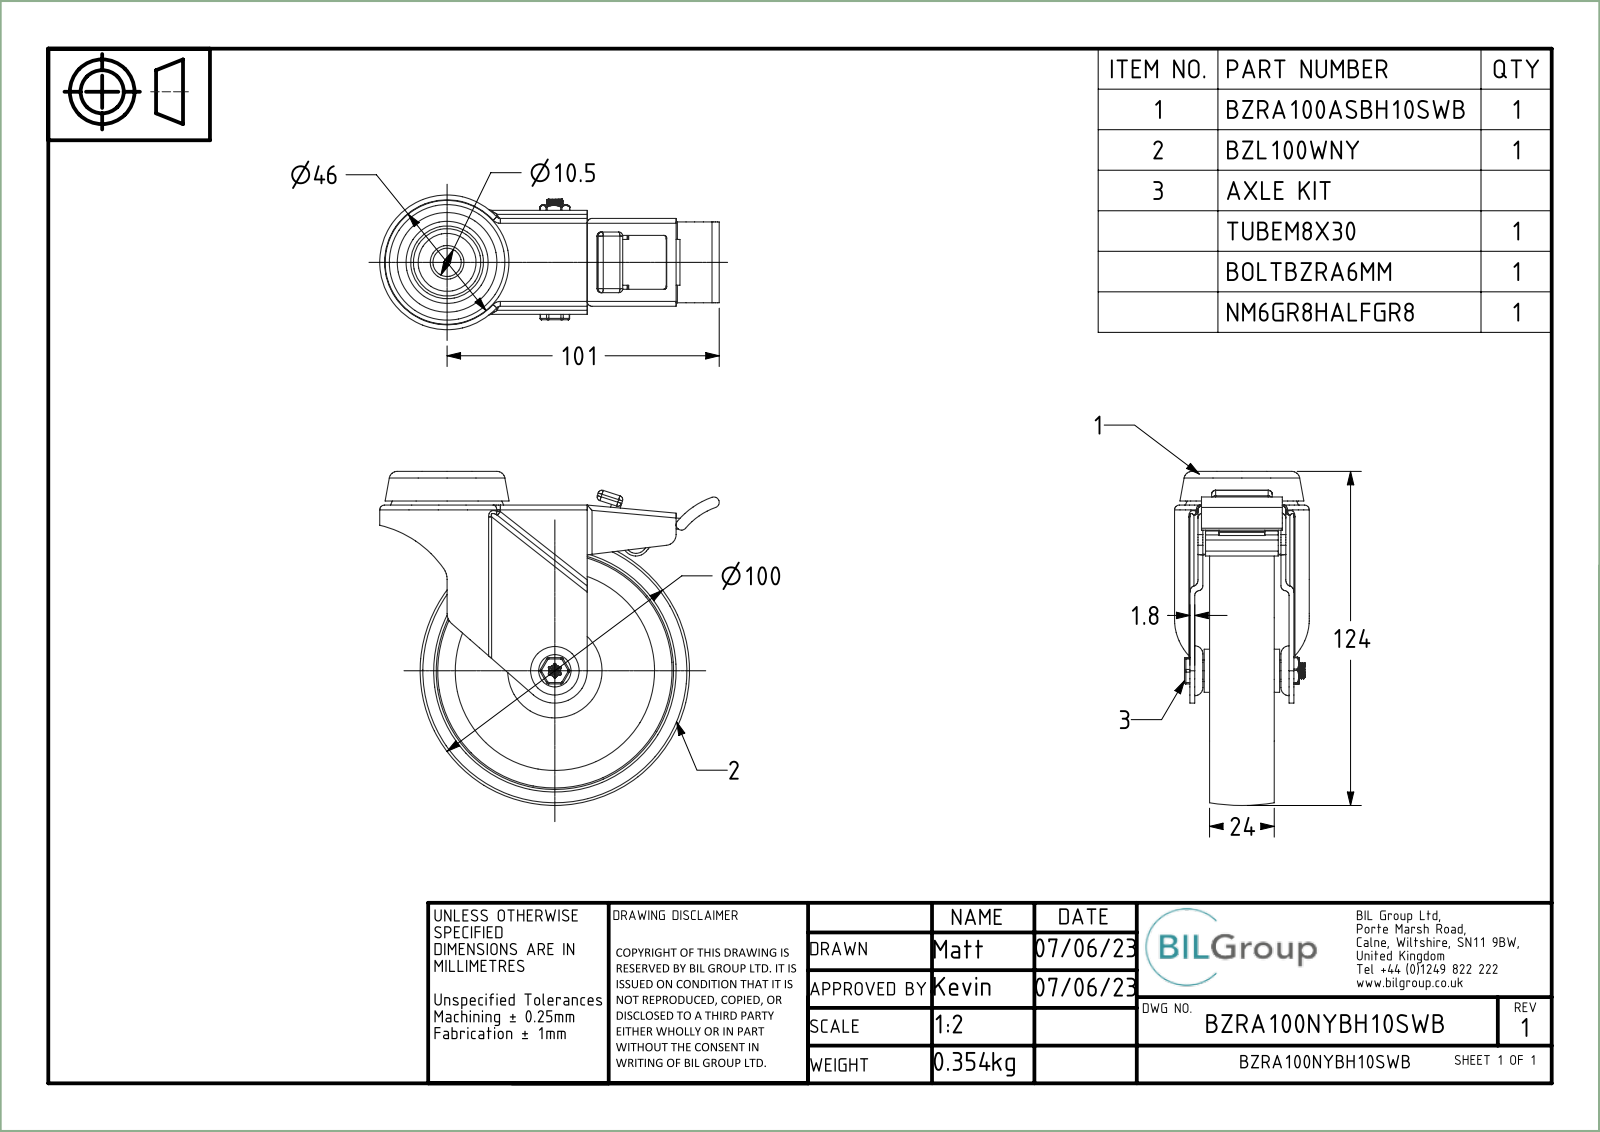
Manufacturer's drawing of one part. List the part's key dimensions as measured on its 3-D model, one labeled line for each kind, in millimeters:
Part name (STEP PRODUCT): BZRA100ASBH10SWB; ZINC PLATED PRESSED STEEL HEAD; ZINC PLATED PRESSED STEEL FORKS; ZINC PLATED PRESSED STEEL BRAKE (+8 more)
STEP written by: Spatial InterOp 3D (CONFIG_CONTROL_DESIGN)
Units: millimetres
Bodies: 9 solids, 620 faces (198 planar, 250 cylindrical, 172 other)
Overall size (bounding box): 126 × 124 × 50
Volume: 113 086 mm³ · Surface area: 73 243 mm²
Round holes (diameter × count): ⌀6 ×1, ⌀6.3 ×1, ⌀6.4 ×1, ⌀8.2 ×1, ⌀8.3 ×1, ⌀10.5 ×1, ⌀10.56 ×1, ⌀30 ×1
Round bosses / shafts (diameter × count): ⌀39 ×1, ⌀18 ×1, ⌀16 ×1, ⌀14.76 ×1, ⌀8 ×1, ⌀7.95 ×1, ⌀5 ×1
Partial cylindrical surfaces — rounded edges, fillets, slot ends (radius × count): R1.8 ×27, R1 ×22, R0.5 ×13, R1.5 ×12, R0.4 ×6, R0.9 ×4, R2 ×4, R5 ×2
Main face-to-face distances: 1.8, 33.8, 4, 3, 12.5, 4.8, 17.3, 21.3, 16.5, 5.5
